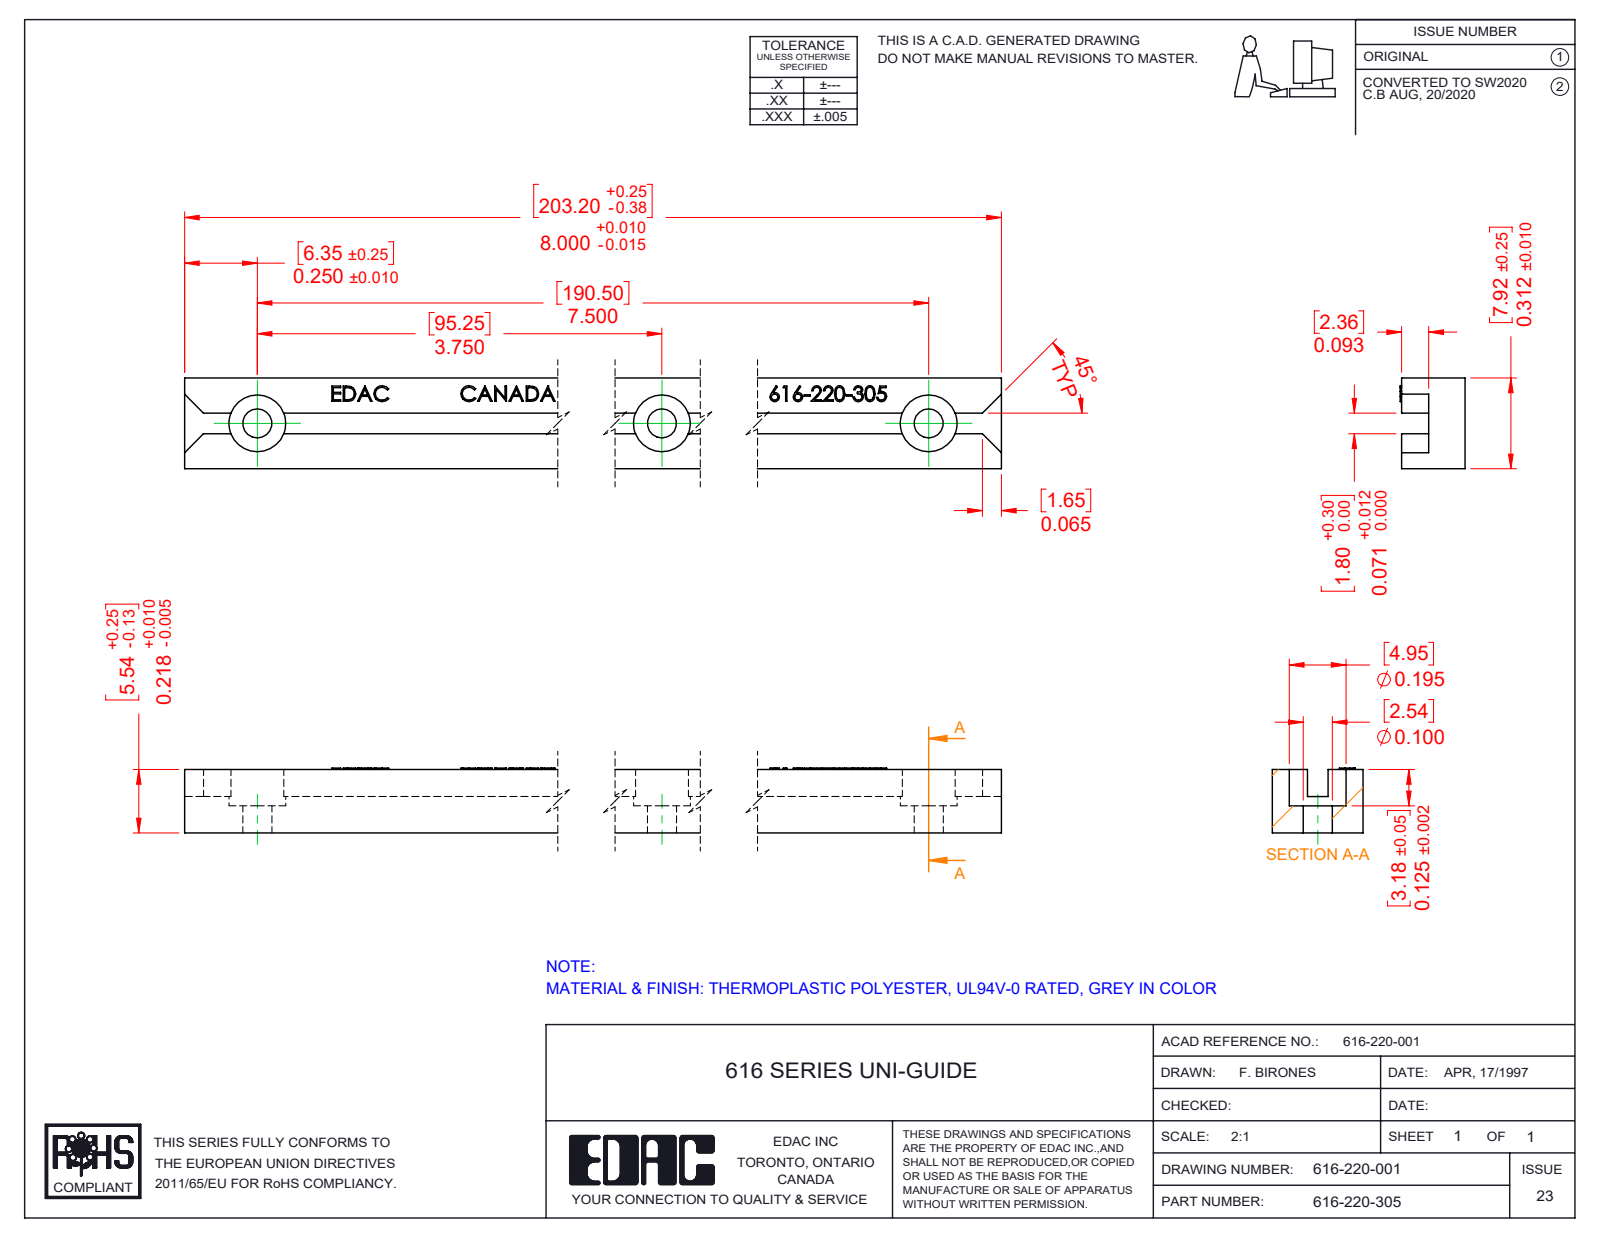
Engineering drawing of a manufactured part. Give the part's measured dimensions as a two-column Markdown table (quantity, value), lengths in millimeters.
| quantity | value |
| --- | --- |
| part name | 616-220-305 |
| STEP written by | SolidWorks 2020 (AUTOMOTIVE_DESIGN) |
| units | millimeters |
| bodies | 1 solid, 294 faces (180 planar, 12 cylindrical, 102 other) |
| overall size | 203.2 × 7.9 × 5.7 |
| volume | 7 880 mm³ |
| surface area | 6 600 mm² |
| round holes (diameter × count) | 2.5 × 3, 5 × 3 |
| main face-to-face distances | 5.5, 7.9, 3, 4.9, 1.8, 2.4, 3.2, 2.4, 0.8, 3.2 |
| hole center spacings | 95.3, 190.5 |
